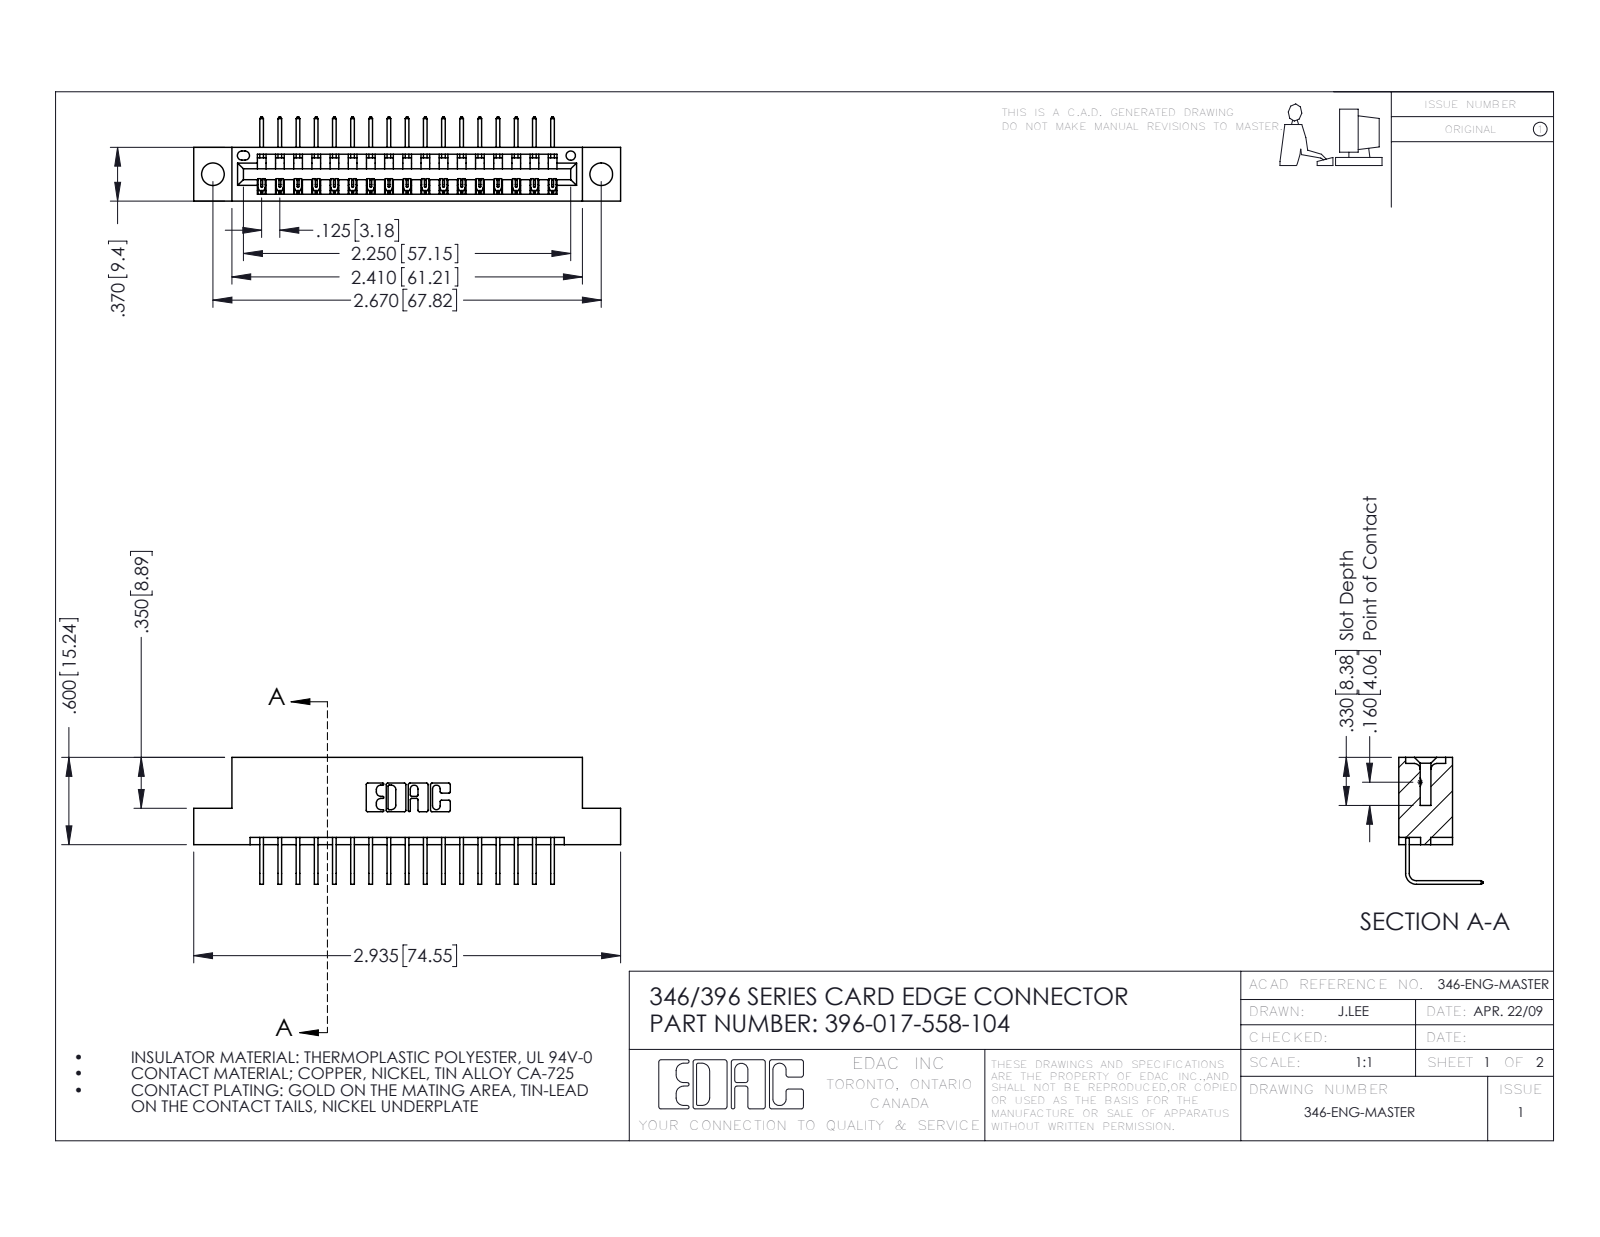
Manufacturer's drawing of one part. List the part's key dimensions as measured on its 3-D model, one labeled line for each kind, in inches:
Part name (STEP PRODUCT): 345-292-001_558 Tail - 2; 346 Part_Flush Mounting Lugs - 0.156 Dia-TH; 396-017-558-104
STEP written by: SolidWorks 2016 (CONFIG_CONTROL_DESIGN)
Units: inches
Bodies: 18 solids, 1142 faces (790 planar, 352 cylindrical, 0 other)
Overall size (bounding box): 2.935 × 0.873 × 0.58
Volume: 0.423 in³ · Surface area: 13.23 in²
Round holes (diameter × count): ⌀0.156 ×2, ⌀0.064 ×1
Partial cylindrical surfaces — rounded edges, fillets, slot ends (radius × count): R0.006 ×34, R0.01 ×22, R0.007 ×6, R0.031 ×6, R0.026 ×3, R0.031 ×2, R0.04 ×2, R0.014 ×1
Main face-to-face distances: 0.322, 0.048, 0.25, 0.37, 0.298, 0.025, 0.072, 0.148, 0.222, 0.1
Hole centre spacings: 0.246, 2.463, 2.67
